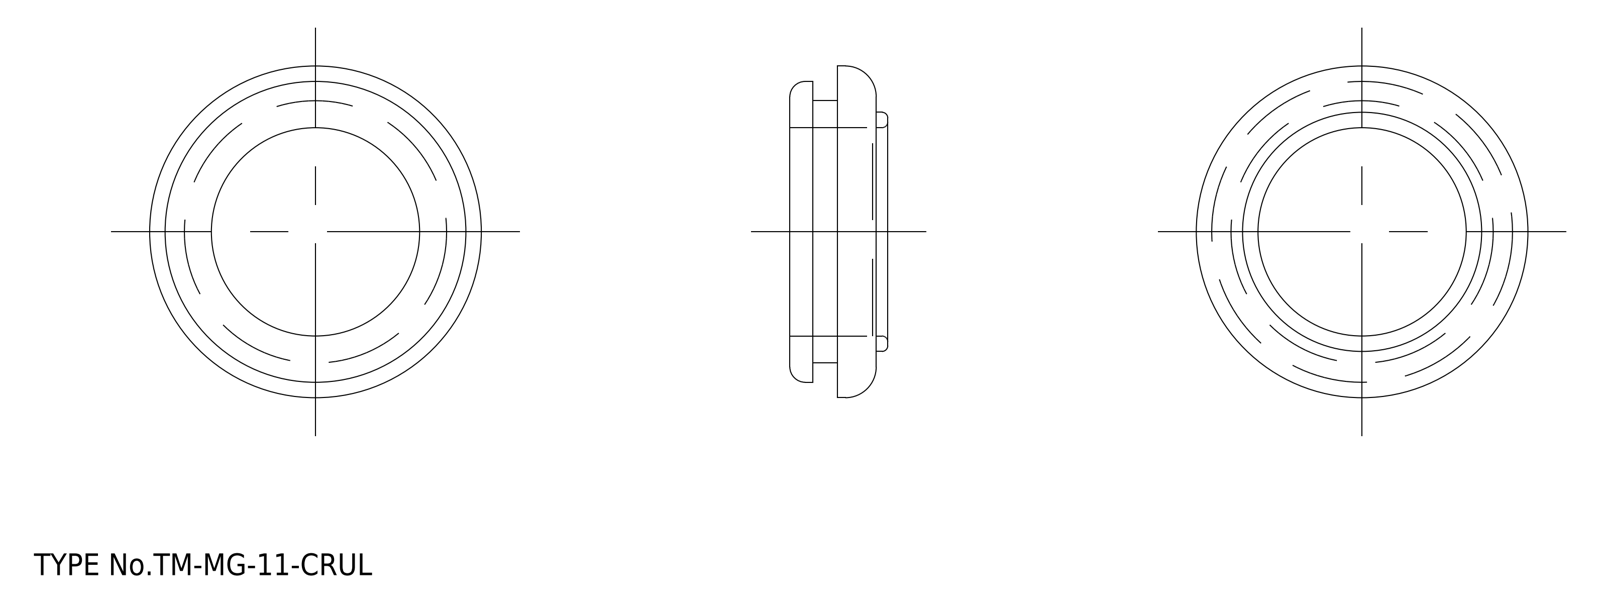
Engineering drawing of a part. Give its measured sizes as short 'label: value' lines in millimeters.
written by: spGate 15.6.1 (AUTOMOTIVE_DESIGN)
unit: mm
bodies: 1 solid, 27 faces (7 planar, 12 cylindrical, 8 other)
size: 43 × 43 × 12.7
volume: 7 332 mm³; area: 5 641 mm²
holes: 1× ⌀27
bosses: 1× ⌀43, 1× ⌀39, 1× ⌀34, 1× ⌀31
face distances: 0.5, 4.5, 5, 6.2, 10.7, 11.2, 3, 3.2, 7.7, 8.2
